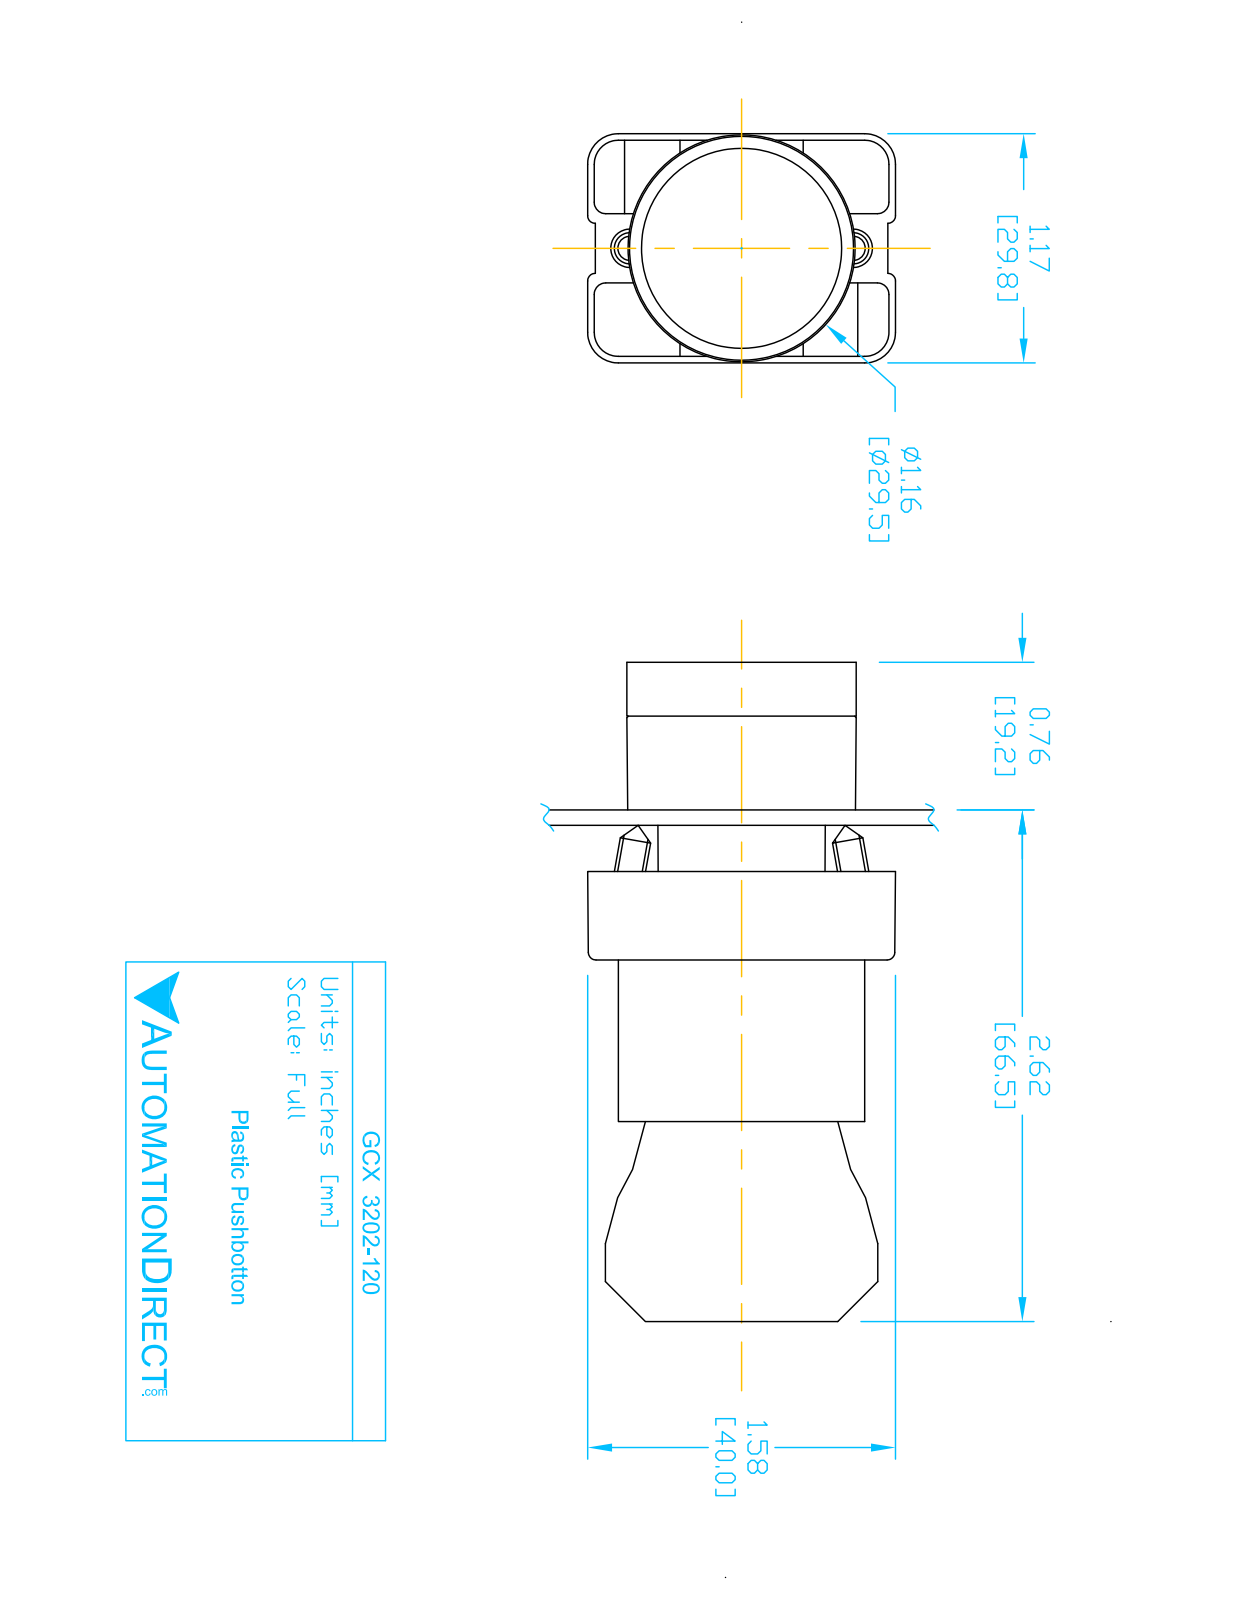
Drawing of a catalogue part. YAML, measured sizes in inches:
part_name: "ecx1040; GCX3202-120; ECX3029-2; ECX1050 (+1 more)"
step_written_by: "SolidWorks 2016 (AUTOMOTIVE_DESIGN)"
units: inches
bodies: {solids: 8, faces: 431, planar: 252, cylindrical: 148, other: 31}
overall_size: [3.319, 1.581, 1.177]
volume: 2.794
surface_area: 38.77
round_holes:
  - {diameter: 0.079, count: 2}
  - {diameter: 0.124, count: 2}
  - {diameter: 0.13, count: 2}
  - {diameter: 0.087, count: 1}
  - {diameter: 0.197, count: 1}
  - {diameter: 0.469, count: 1}
  - {diameter: 0.878, count: 1}
  - {diameter: 0.888, count: 1}
  - {diameter: 1.024, count: 1}
round_bosses_or_shafts:
  - {diameter: 0.157, count: 4}
  - {diameter: 1.175, count: 1}
  - {diameter: 1.004, count: 1}
  - {diameter: 0.945, count: 1}
  - {diameter: 0.856, count: 1}
  - {diameter: 0.78, count: 1}
  - {diameter: 0.504, count: 1}
partial_cylinders:
  - {radius: 0.059, count: 24}
  - {radius: 0.041, count: 12}
  - {radius: 0.124, count: 12}
  - {radius: 0.157, count: 12}
  - {radius: 0.039, count: 8}
  - {radius: 0.128, count: 2}
  - {radius: 0.02, count: 1}
  - {radius: 0.063, count: 1}
face_to_face_distances: [0.827, 0.579, 2.02, 1.193, 1.171, 0.276, 2.295, 1.469, 0.031, 0.033]
hole_center_spacings: [0.236, 0.544, 0.472, 0.49]
